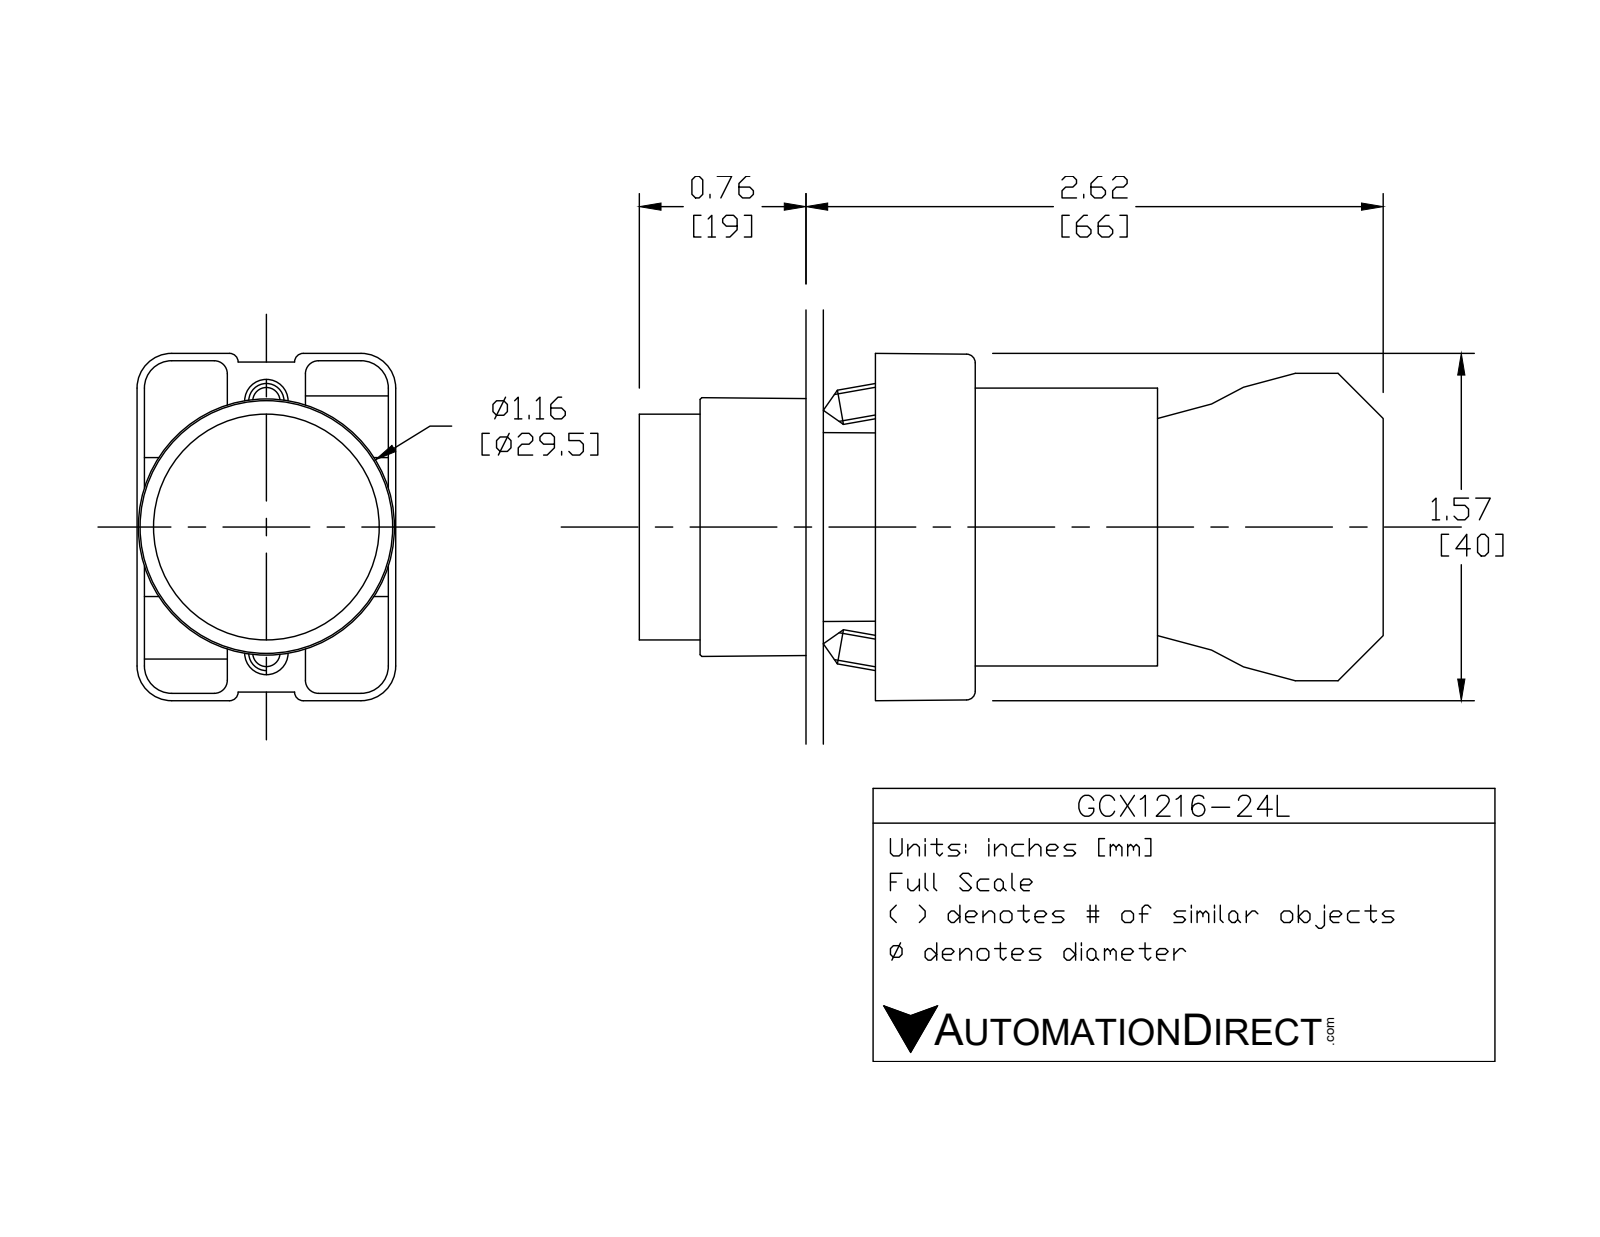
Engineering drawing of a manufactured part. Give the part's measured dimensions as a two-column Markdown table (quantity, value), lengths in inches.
| quantity | value |
| --- | --- |
| part name | ecx1040; GCX1216L OPERATOR; ECX1050; GCX1216-24L (+1 more) |
| STEP written by | SolidWorks 2016 (AUTOMOTIVE_DESIGN) |
| units | inches |
| bodies | 7 solids, 425 faces (250 planar, 144 cylindrical, 31 other) |
| overall size | 3.319 × 1.581 × 1.177 |
| volume | 2.721 in³ |
| surface area | 36.32 in² |
| round holes (diameter × count) | 0.079 × 2, 0.124 × 2, 0.13 × 2, 0.087 × 1, 0.197 × 1, 0.469 × 1, 0.878 × 1, 0.888 × 1, 1.024 × 1 |
| round bosses / shafts (diameter × count) | 0.157 × 4, 1.175 × 1, 1.004 × 1, 0.945 × 1, 0.856 × 1, 0.78 × 1, 0.504 × 1 |
| partial cylindrical surfaces (radius × count) | 0.059 × 24, 0.041 × 12, 0.124 × 12, 0.157 × 12, 0.039 × 8, 0.128 × 2, 0.02 × 1, 0.063 × 1 |
| main face-to-face distances | 0.827, 0.579, 1.171, 2.02, 1.193, 0.031, 0.033, 0.573, 1.165, 0.593 |
| hole center spacings | 0.236, 0.544, 0.472, 0.49 |
